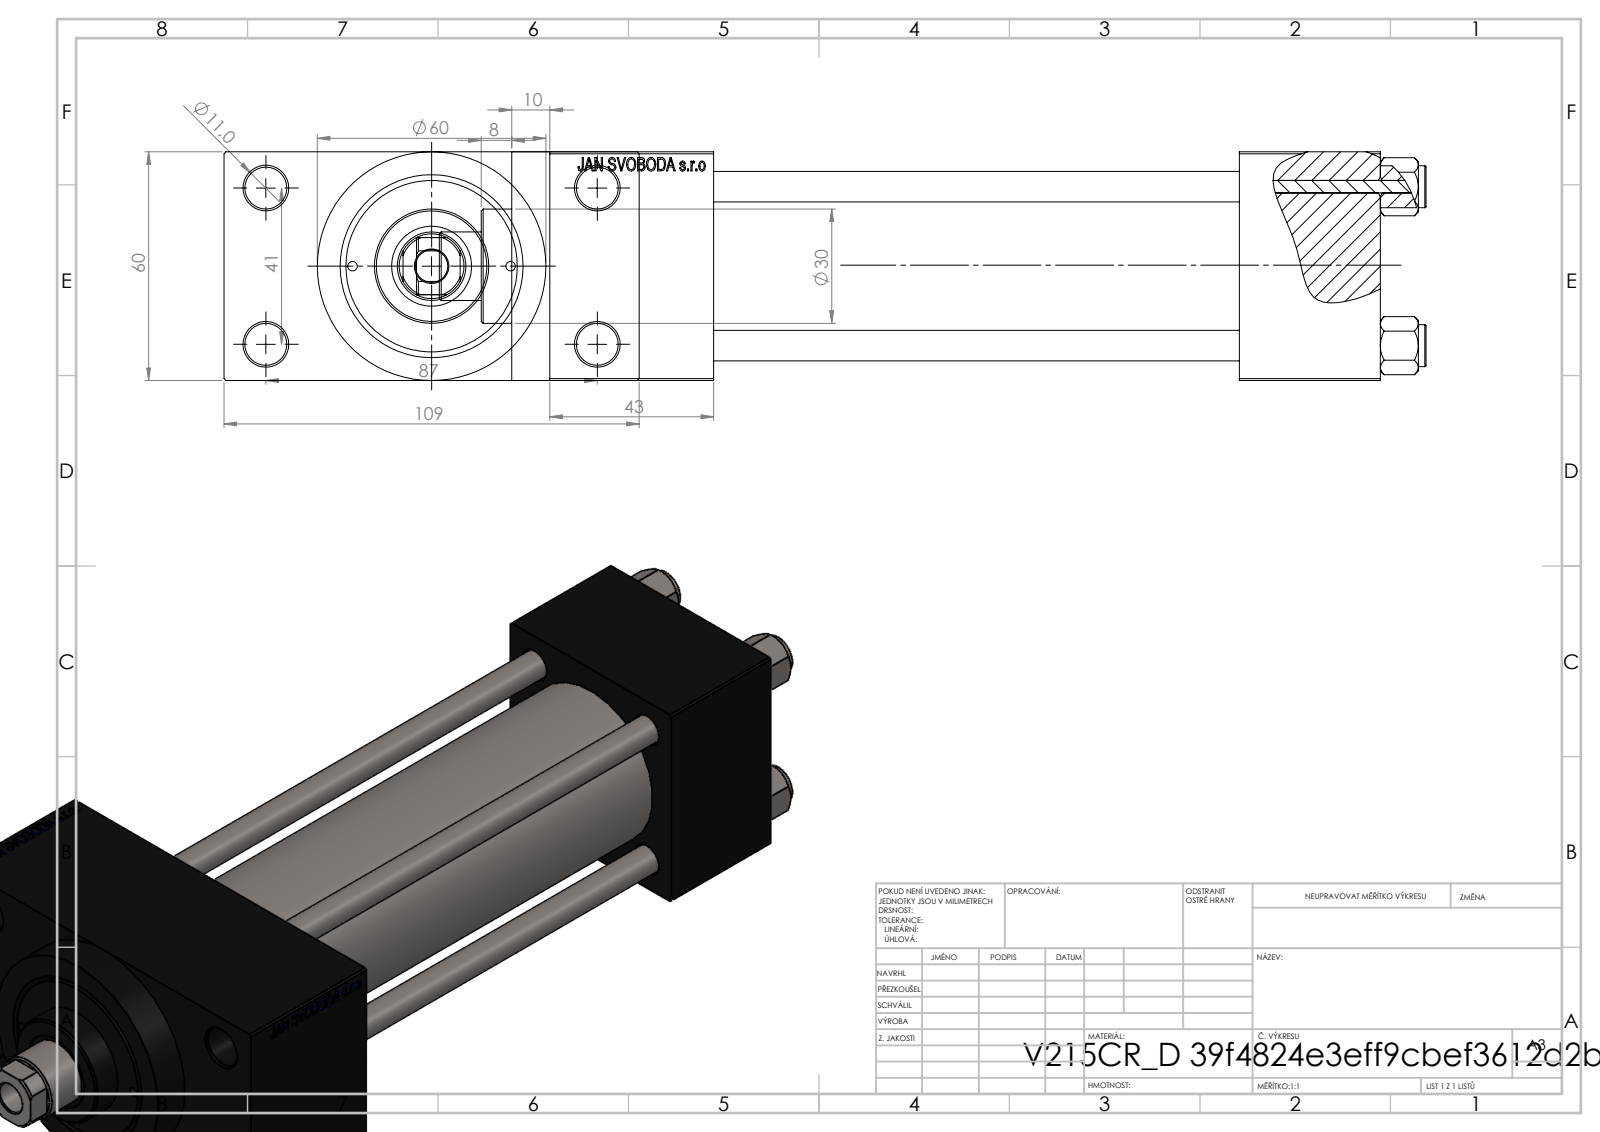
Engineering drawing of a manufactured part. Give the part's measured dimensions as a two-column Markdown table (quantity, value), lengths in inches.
| quantity | value |
| --- | --- |
| part name | V215CR_D_Body; V215CR_D_TYCINKA; V215_VC_A; V215CR_VCP_D (+1 more) |
| STEP written by | SolidWorks 2019 (CONFIG_CONTROL_DESIGN) |
| units | inches |
| bodies | 11 solids, 1112 faces (500 planar, 92 cylindrical, 520 other) |
| overall size | 10.433 × 4.291 × 2.362 |
| volume | 35.47 in³ |
| surface area | 242.9 in² |
| round holes (diameter × count) | 0.315 × 4, 0.433 × 4, 0.098 × 2, 0.276 × 2, 0.656 × 2, 0.945 × 2, 0.335 × 1, 0.709 × 1, 0.827 × 1, 1.22 × 1, 1.575 × 1, 1.772 × 1 |
| round bosses / shafts (diameter × count) | 0.433 × 4, 2.362 × 1, 1.811 × 1, 1.181 × 1 |
| partial cylindrical surfaces (radius × count) | 0.335 × 1 |
| main face-to-face distances | 2.362, 5.433, 0.965, 3.327, 1.457, 6.89, 8.583, 7.126, 1.693, 7.273 |
| hole center spacings | 0.821, 0.892, 1.161, 1.206, 1.642, 1.832, 1.856, 1.893 |
